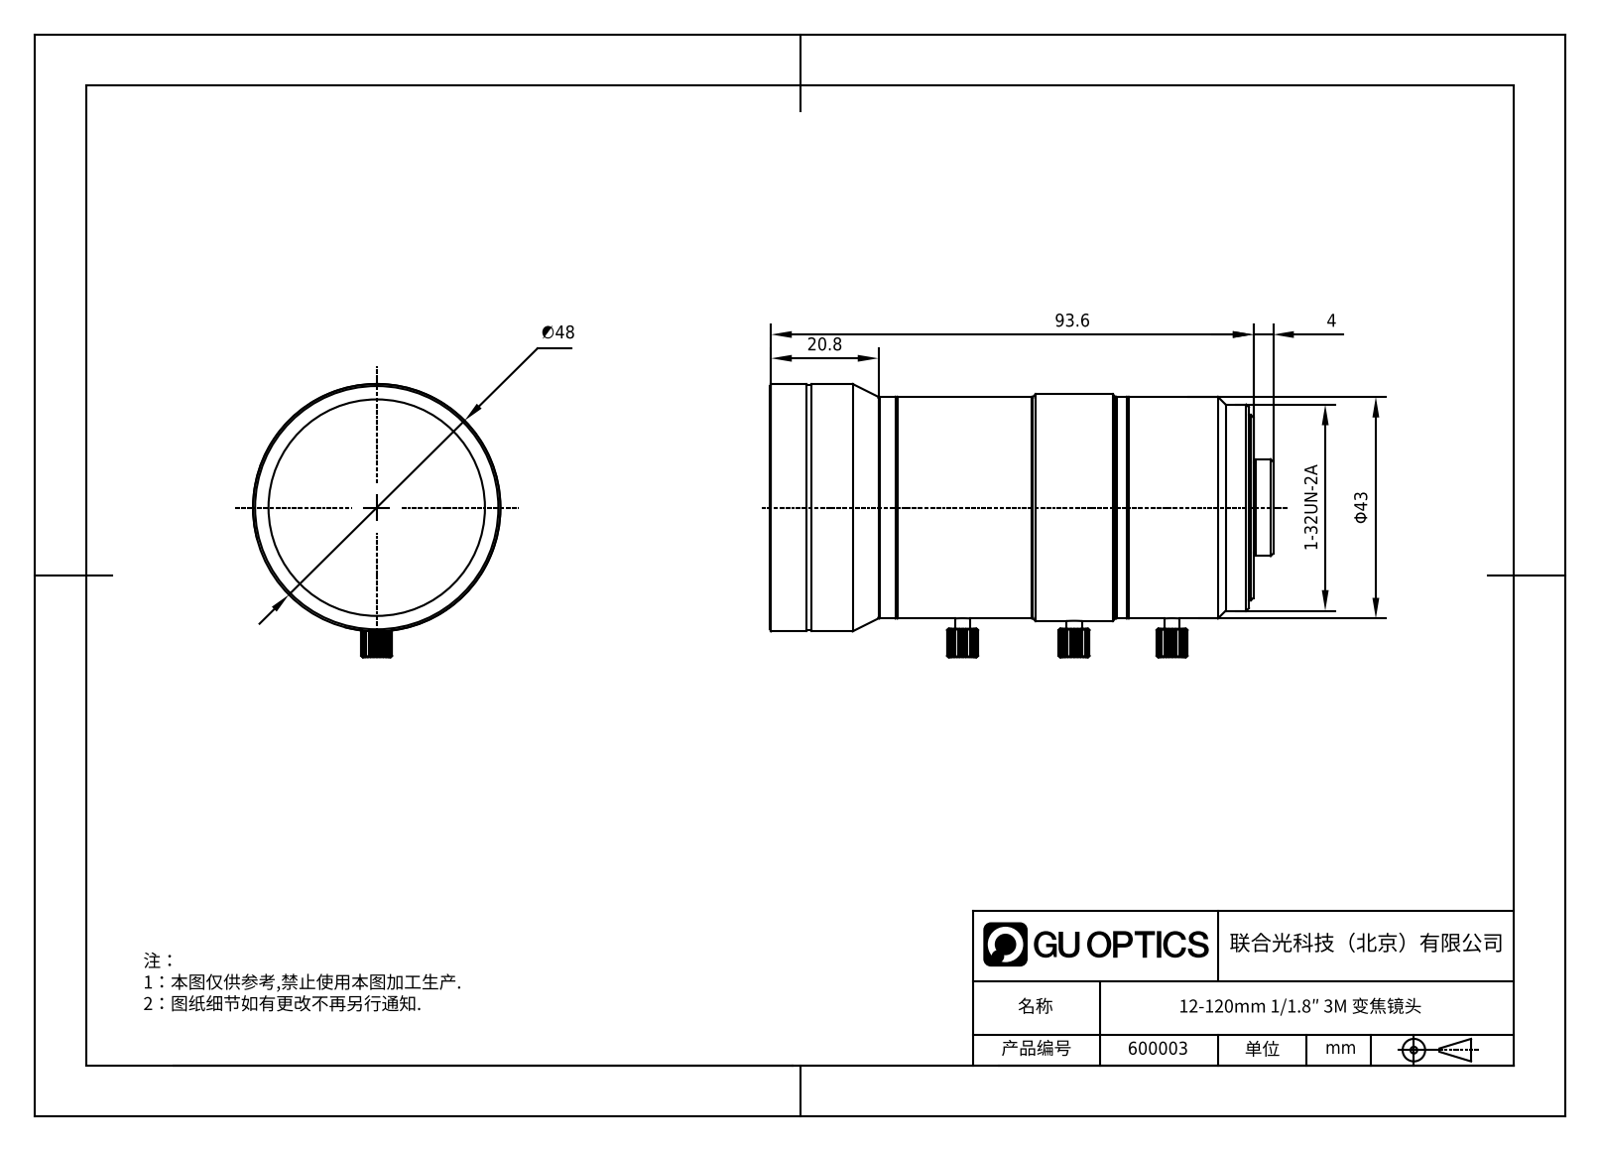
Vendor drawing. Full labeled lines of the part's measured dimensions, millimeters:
Part name (STEP PRODUCT): 640003
STEP written by: SolidWorks 2020 (CONFIG_CONTROL_DESIGN)
Units: millimetres
Bodies: 2 solids, 474 faces (407 planar, 33 cylindrical, 34 other)
Overall size (bounding box): 97.63 × 53 × 48
Volume: 125 367 mm³ · Surface area: 19 760 mm²
Round holes (diameter × count): ⌀12 ×1, ⌀42 ×1
Round bosses / shafts (diameter × count): ⌀3 ×3, ⌀48 ×1, ⌀47.6 ×1, ⌀43 ×1, ⌀40 ×1, ⌀36 ×1, ⌀18.8 ×1, ⌀17.5 ×1
Partial cylindrical surfaces — rounded edges, fillets, slot ends (radius × count): R22 ×1
Main face-to-face distances: 43.76, 93.78, 43.74, 43.78, 3.85, 92.9, 0.88, 1.73, 97.63, 4.73
